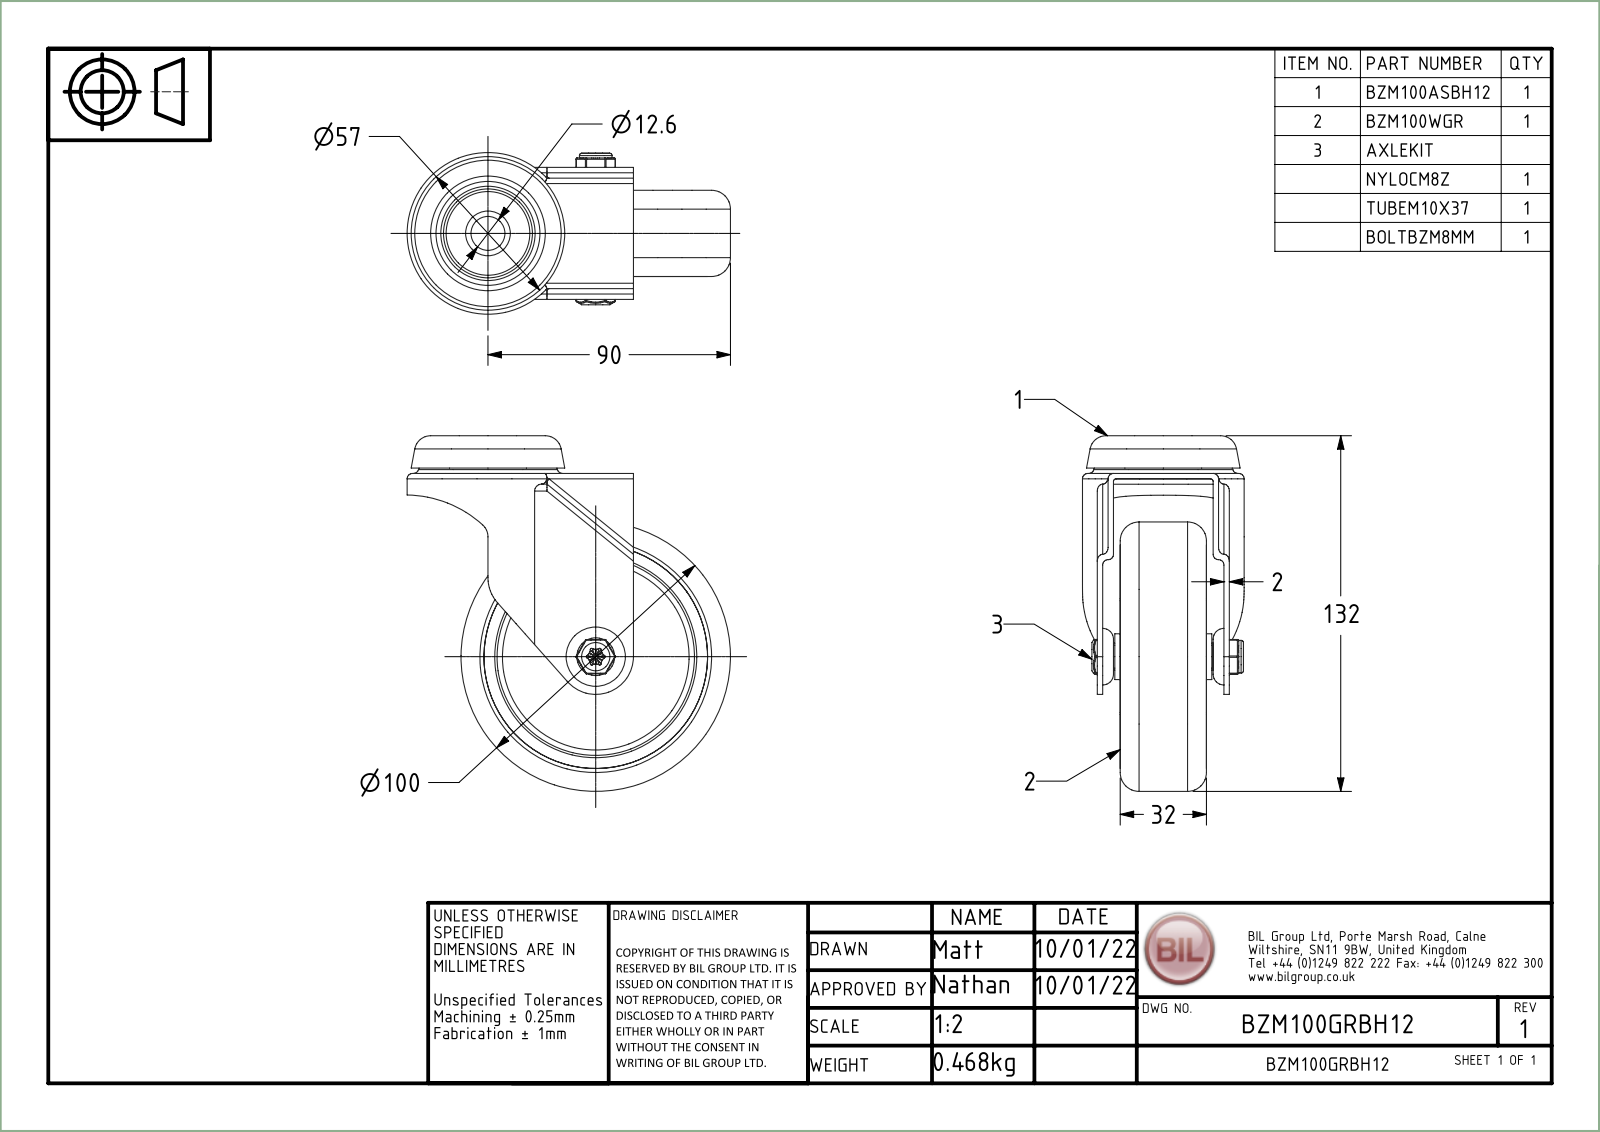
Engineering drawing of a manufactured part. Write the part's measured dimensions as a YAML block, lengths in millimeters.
part_name: "BZM100ASBH12; ZINC PLATED PRESSED STEEL FORKS; ZINC PLATED PRESSED STEEL HEAD; BZM100GRBH12 (+8 more)"
step_written_by: "Spatial InterOp 3D (AUTOMOTIVE_DESIGN)"
units: millimeters
bodies: {solids: 8, faces: 394, planar: 66, cylindrical: 176, other: 152}
overall_size: [132, 120, 60]
volume: 187020
surface_area: 89984
round_holes:
  - {diameter: 8, count: 1}
  - {diameter: 8.25, count: 1}
  - {diameter: 8.3, count: 1}
  - {diameter: 8.6, count: 1}
  - {diameter: 10.2, count: 1}
  - {diameter: 10.3, count: 1}
  - {diameter: 12.6, count: 1}
  - {diameter: 83, count: 1}
round_bosses_or_shafts:
  - {diameter: 100, count: 1}
  - {diameter: 48, count: 1}
  - {diameter: 30, count: 1}
  - {diameter: 17, count: 1}
  - {diameter: 12.1, count: 1}
  - {diameter: 10, count: 1}
  - {diameter: 6, count: 1}
partial_cylinders:
  - {radius: 0.5, count: 30}
  - {radius: 2, count: 22}
  - {radius: 1, count: 6}
  - {radius: 14, count: 2}
  - {radius: 2.75, count: 1}
  - {radius: 6, count: 1}
  - {radius: 28, count: 1}
  - {radius: 30, count: 1}
face_to_face_distances: [2, 4, 21.75, 27.25, 5.5, 43, 40.5, 13.25, 8.5, 18.75]
